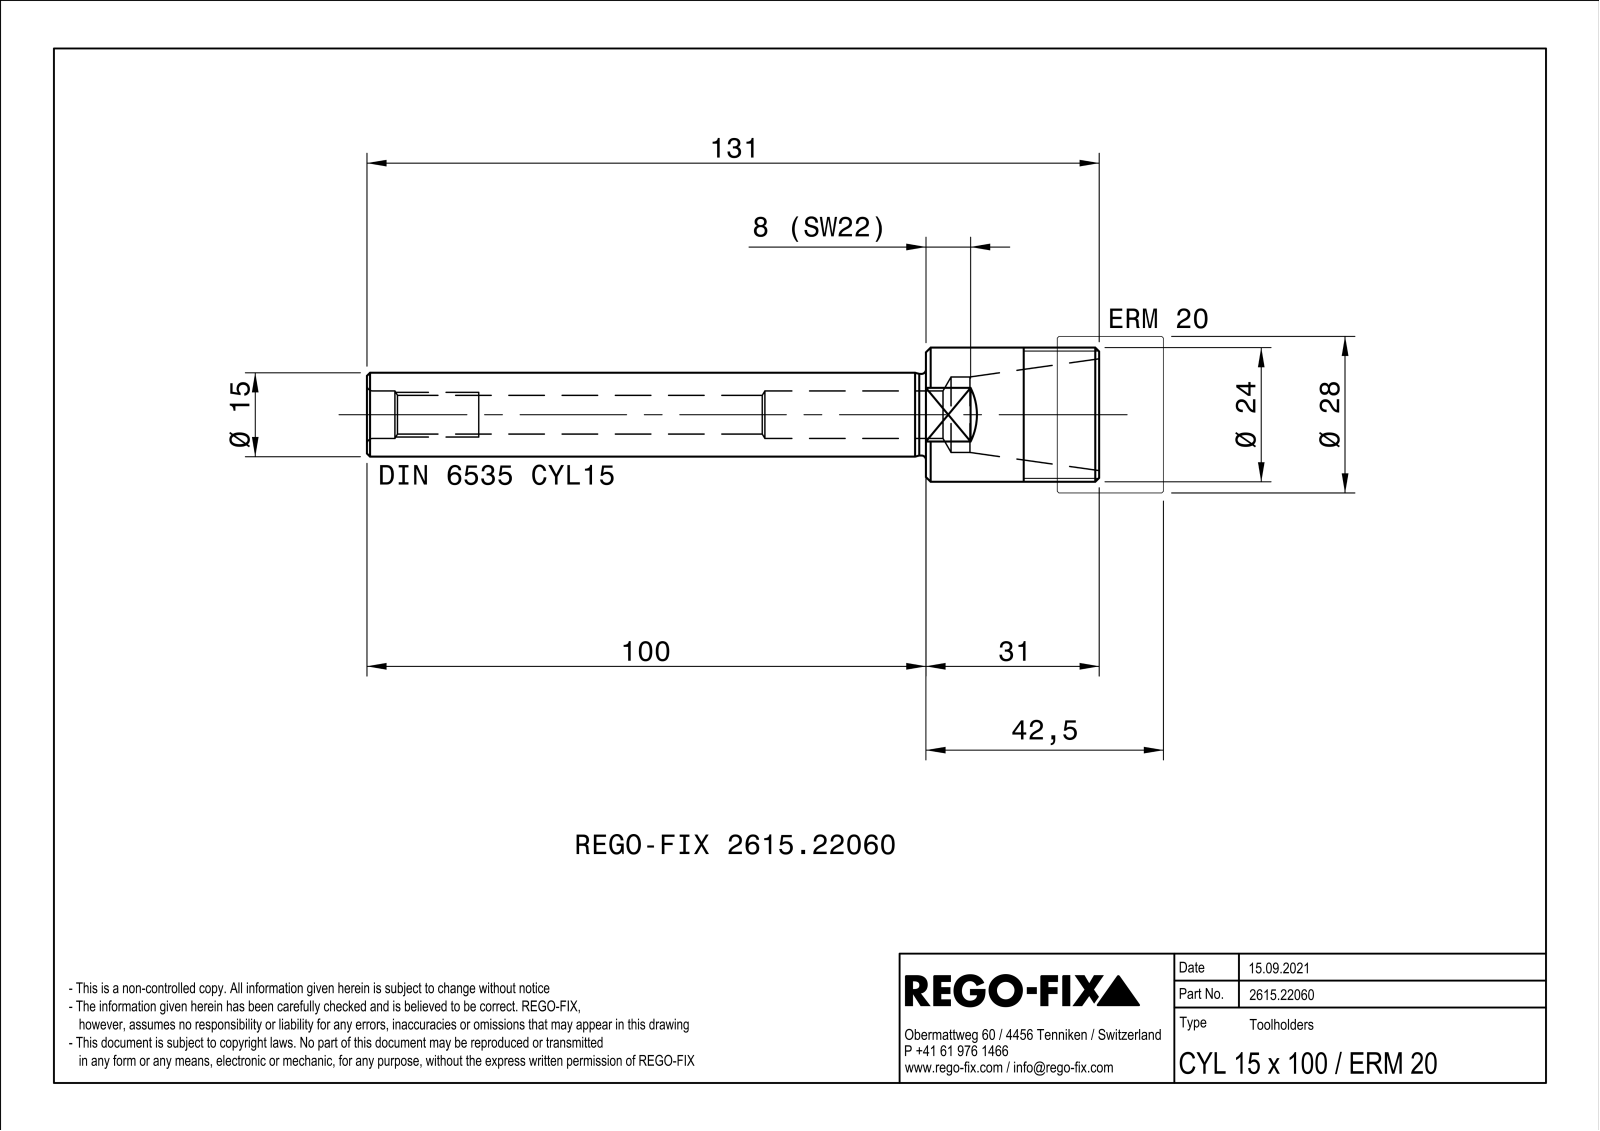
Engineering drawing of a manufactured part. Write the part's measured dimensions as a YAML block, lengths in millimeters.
part_name: "NOCUT"
step_written_by: "SIEMENS PLM Software Solid Edge ST10 (AUTOMOTIVE_DESIGN)"
units: millimeters
bodies: {solids: 1, faces: 30, planar: 9, cylindrical: 9, other: 12}
overall_size: [131, 24, 24]
volume: 21148
surface_area: 11380
round_holes:
  - {diameter: 6.92, count: 1}
  - {diameter: 8.5, count: 1}
  - {diameter: 13.5, count: 1}
round_bosses_or_shafts:
  - {diameter: 24, count: 1}
  - {diameter: 15, count: 1}
  - {diameter: 14.6, count: 1}
face_to_face_distances: [31, 22, 131, 100, 4.95]
